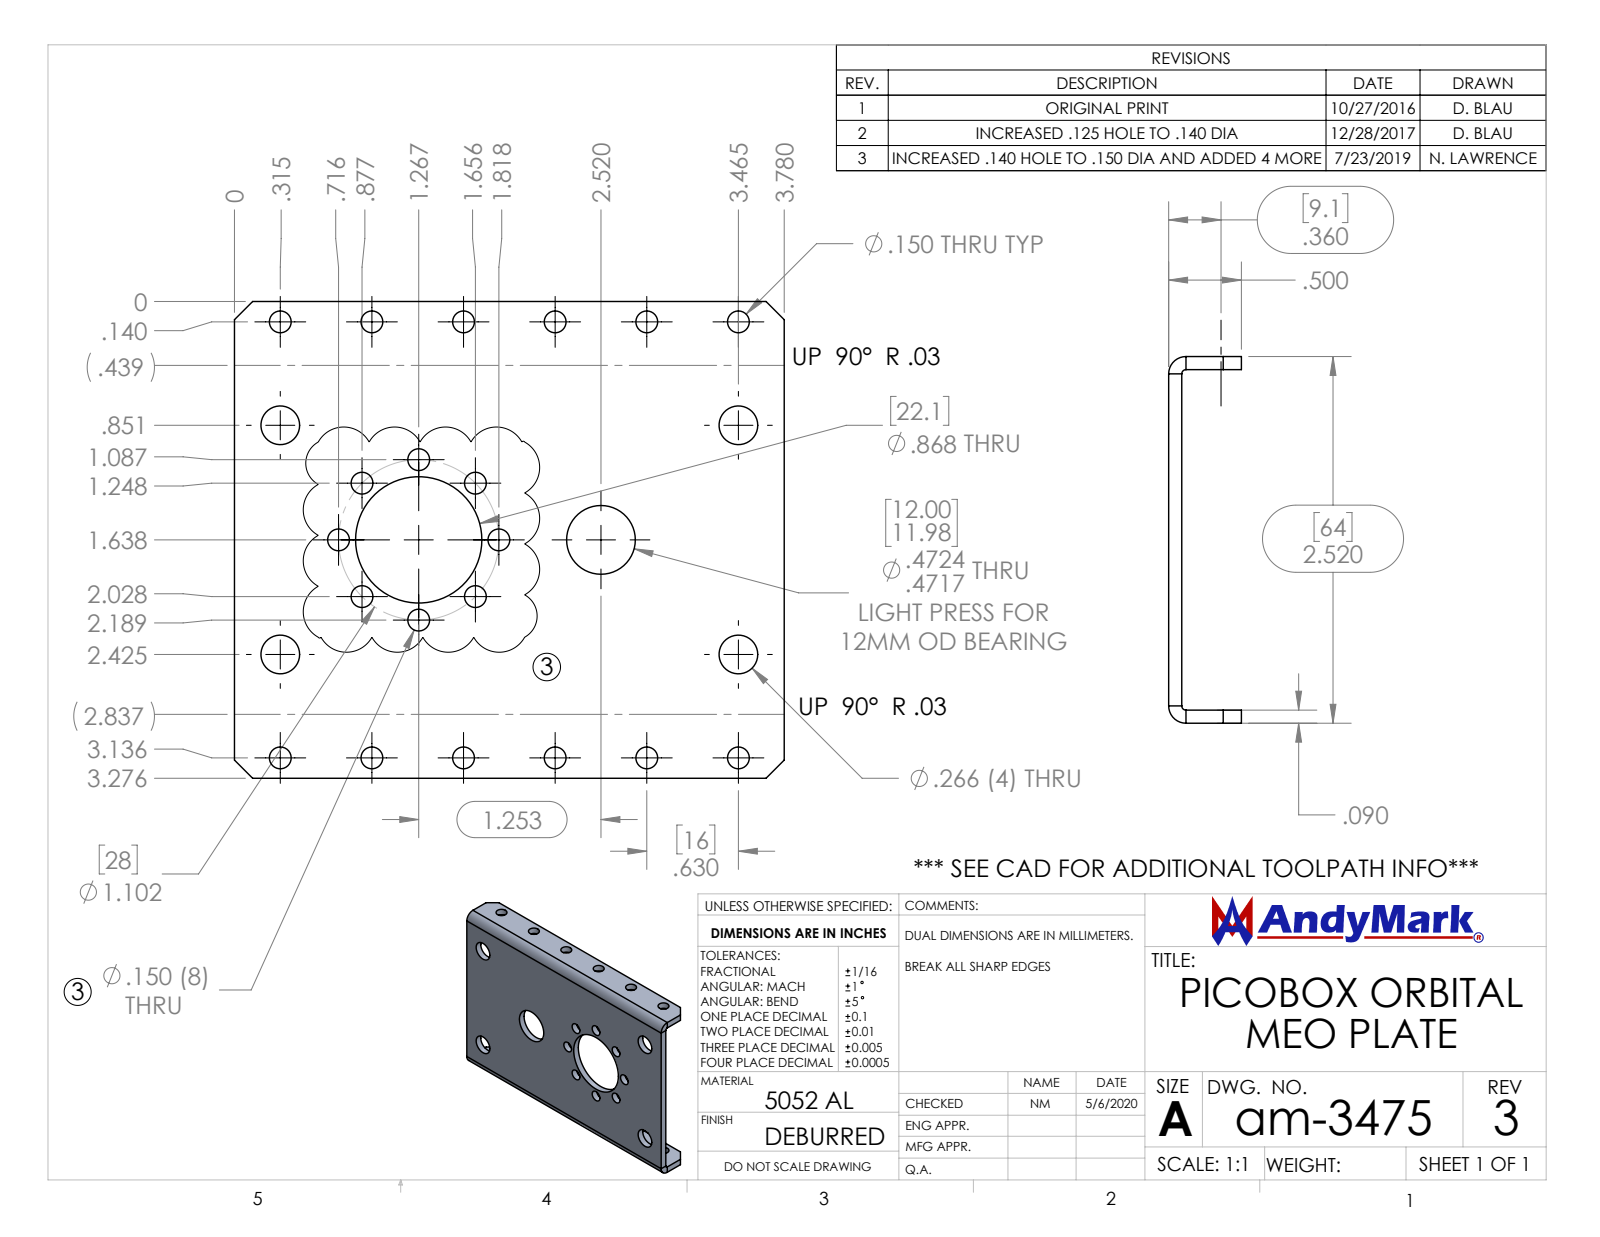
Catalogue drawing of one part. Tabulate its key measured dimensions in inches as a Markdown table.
| quantity | value |
| --- | --- |
| part name | am-3475 PicoBox Orbital MEO Plate |
| STEP written by | SolidWorks 2019 (AUTOMOTIVE_DESIGN) |
| units | inches |
| bodies | 1 solid, 52 faces (22 planar, 30 cylindrical, 0 other) |
| overall size | 3.78 × 2.52 × 0.5 |
| volume | 0.991 in³ |
| surface area | 24.79 in² |
| round holes (diameter × count) | 0.15 × 14, 0.266 × 4, 0.472 × 1, 0.868 × 1 |
| partial cylindrical surfaces (radius × count) | 0.029 × 2, 0.119 × 2 |
| main face-to-face distances | 0.09, 2.43, 2.52, 2.339, 0.41, 0.5, 3.78 |
| hole center spacings | 0.422, 0.551, 0.78, 1.019, 0.63, 1.102, 1.26, 1.89 |
